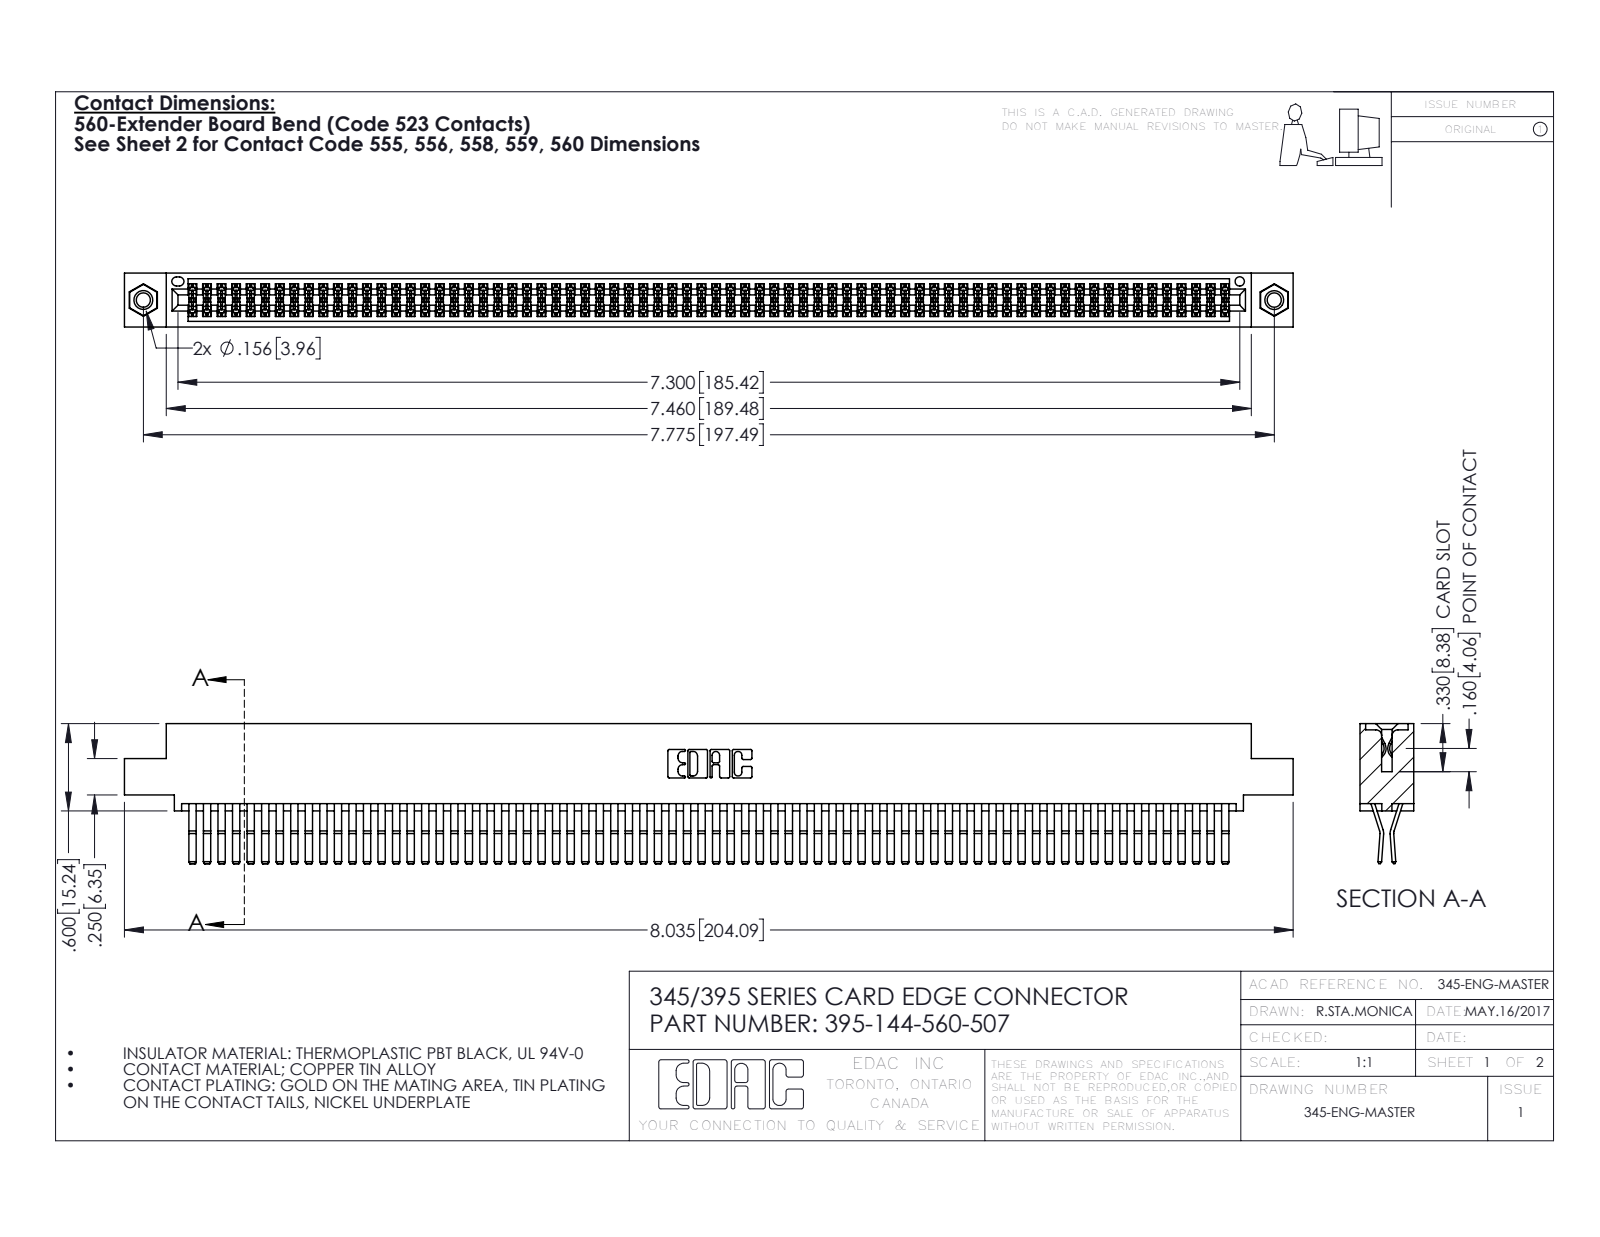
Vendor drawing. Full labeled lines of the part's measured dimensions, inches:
Part name (STEP PRODUCT): 345-292-001_560 Tail; 395-144-560-507; 345 Part_0.110 Offset - 0.156 Dia-TI; 345-250-001_345-250-005-103
STEP written by: SolidWorks 2016 (CONFIG_CONTROL_DESIGN)
Units: inches
Bodies: 147 solids, 7678 faces (4868 planar, 2794 cylindrical, 16 other)
Overall size (bounding box): 8.035 × 0.962 × 0.37
Volume: 1.279 in³ · Surface area: 52.88 in²
Round holes (diameter × count): ⌀0.098 ×2, ⌀0.125 ×2, ⌀0.156 ×2, ⌀0.064 ×1
Round bosses / shafts (diameter × count): ⌀0.155 ×2
Partial cylindrical surfaces — rounded edges, fillets, slot ends (radius × count): R0.006 ×216, R0.01 ×22, R0.007 ×6, R0.031 ×6, R0.026 ×3, R0.01 ×2, R0.014 ×2, R0.019 ×2
Main face-to-face distances: 0.025, 0.072, 0.298, 0.37, 0.2, 0.098, 0.272, 0.225, 0.175, 0.149
Hole centre spacings: 0.27, 7.539, 7.775
